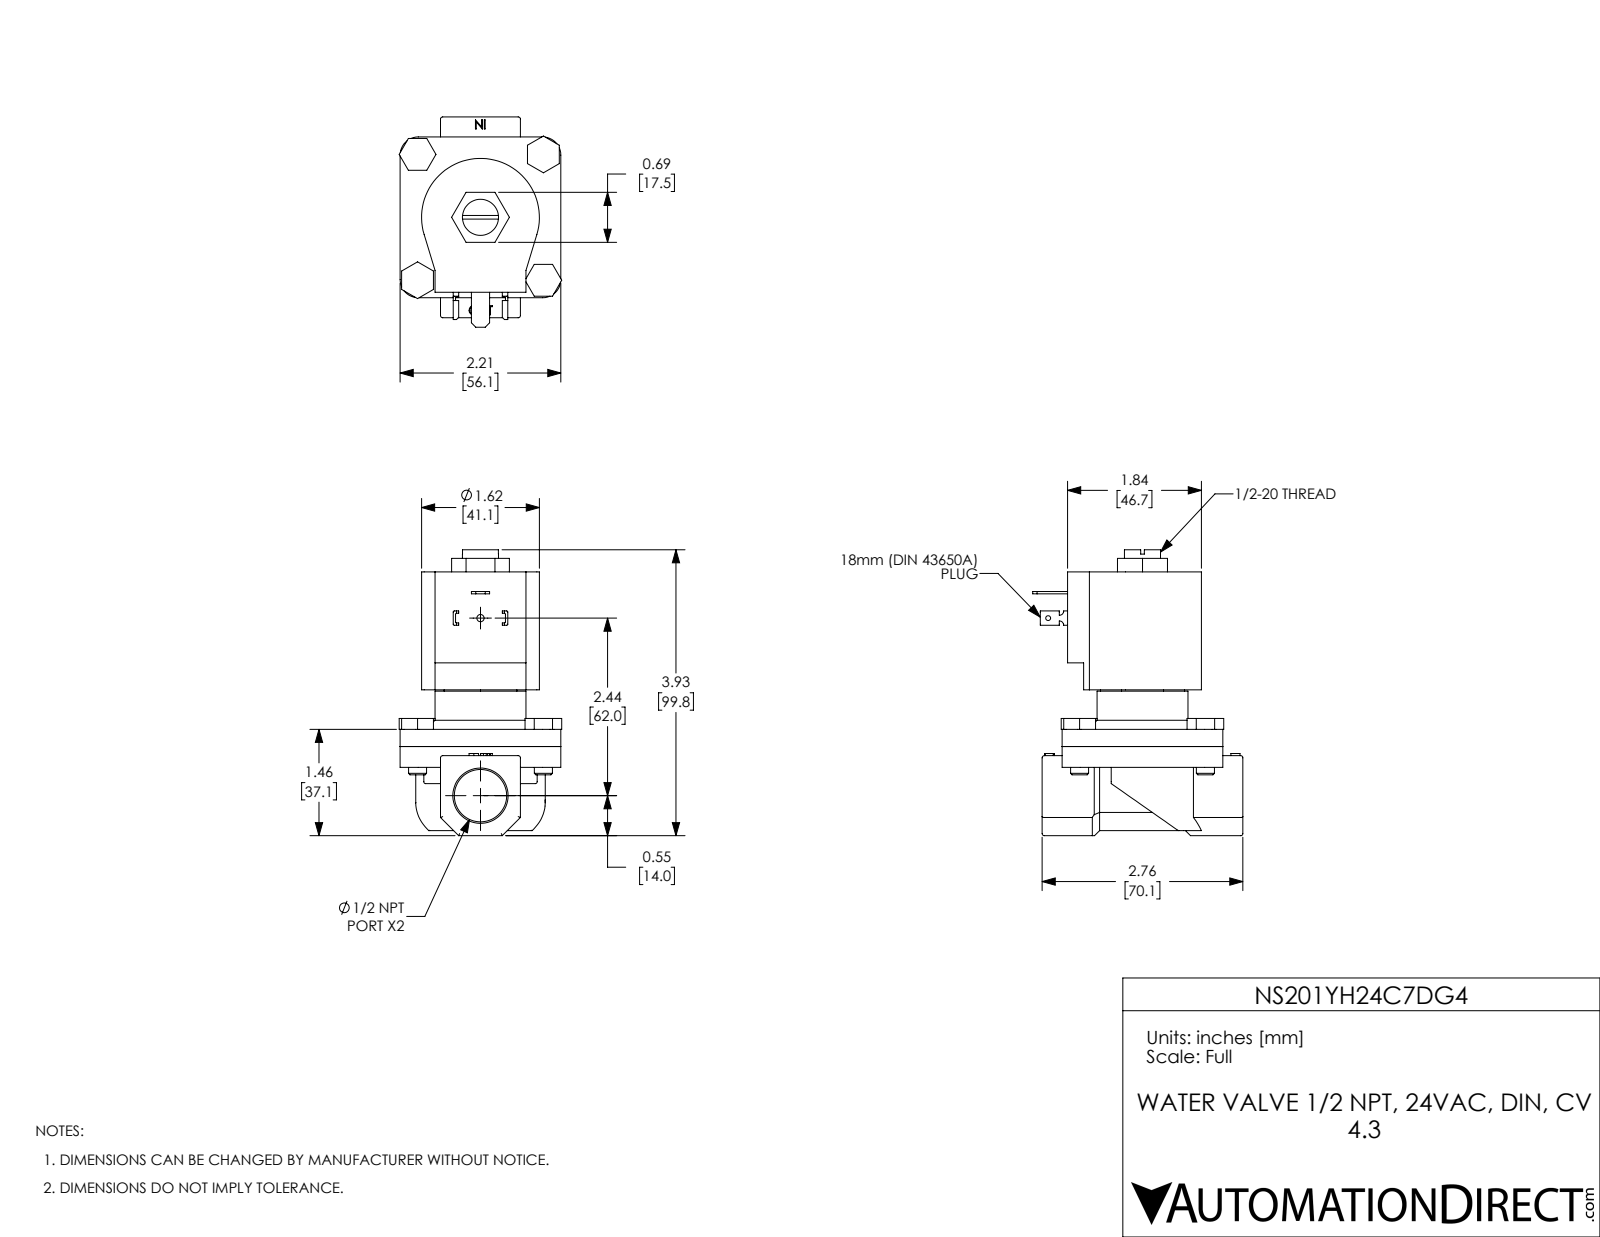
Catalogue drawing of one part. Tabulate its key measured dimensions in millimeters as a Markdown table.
| quantity | value |
| --- | --- |
| part name | NS201YH24C7DG4 |
| STEP written by | SolidWorks 2024 (CONFIG_CONTROL_DESIGN) |
| units | millimeters |
| bodies | 11 solids, 330 faces (196 planar, 99 cylindrical, 35 other) |
| overall size | 99.8 × 73.4 × 56.8 |
| volume | 160 900 mm³ |
| surface area | 40 930 mm² |
| round holes (diameter × count) | 6.4 × 4, 1.7 × 1, 2.5 × 1, 12.6 × 1, 13 × 1, 18.3 × 1, 29.3 × 1 |
| round bosses / shafts (diameter × count) | 6.3 × 4, 31.8 × 1 |
| partial cylindrical surfaces (radius × count) | 0.8 × 15, 0.4 × 8, 6.4 × 4, 1.5 × 2, 20.6 × 1, 22.6 × 1 |
| main face-to-face distances | 6, 6, 61, 61, 54.9, 14.1, 42, 7.3, 7.3, 13.3 |
| hole center spacings | 31.1, 43.9, 62.1, 62 |
